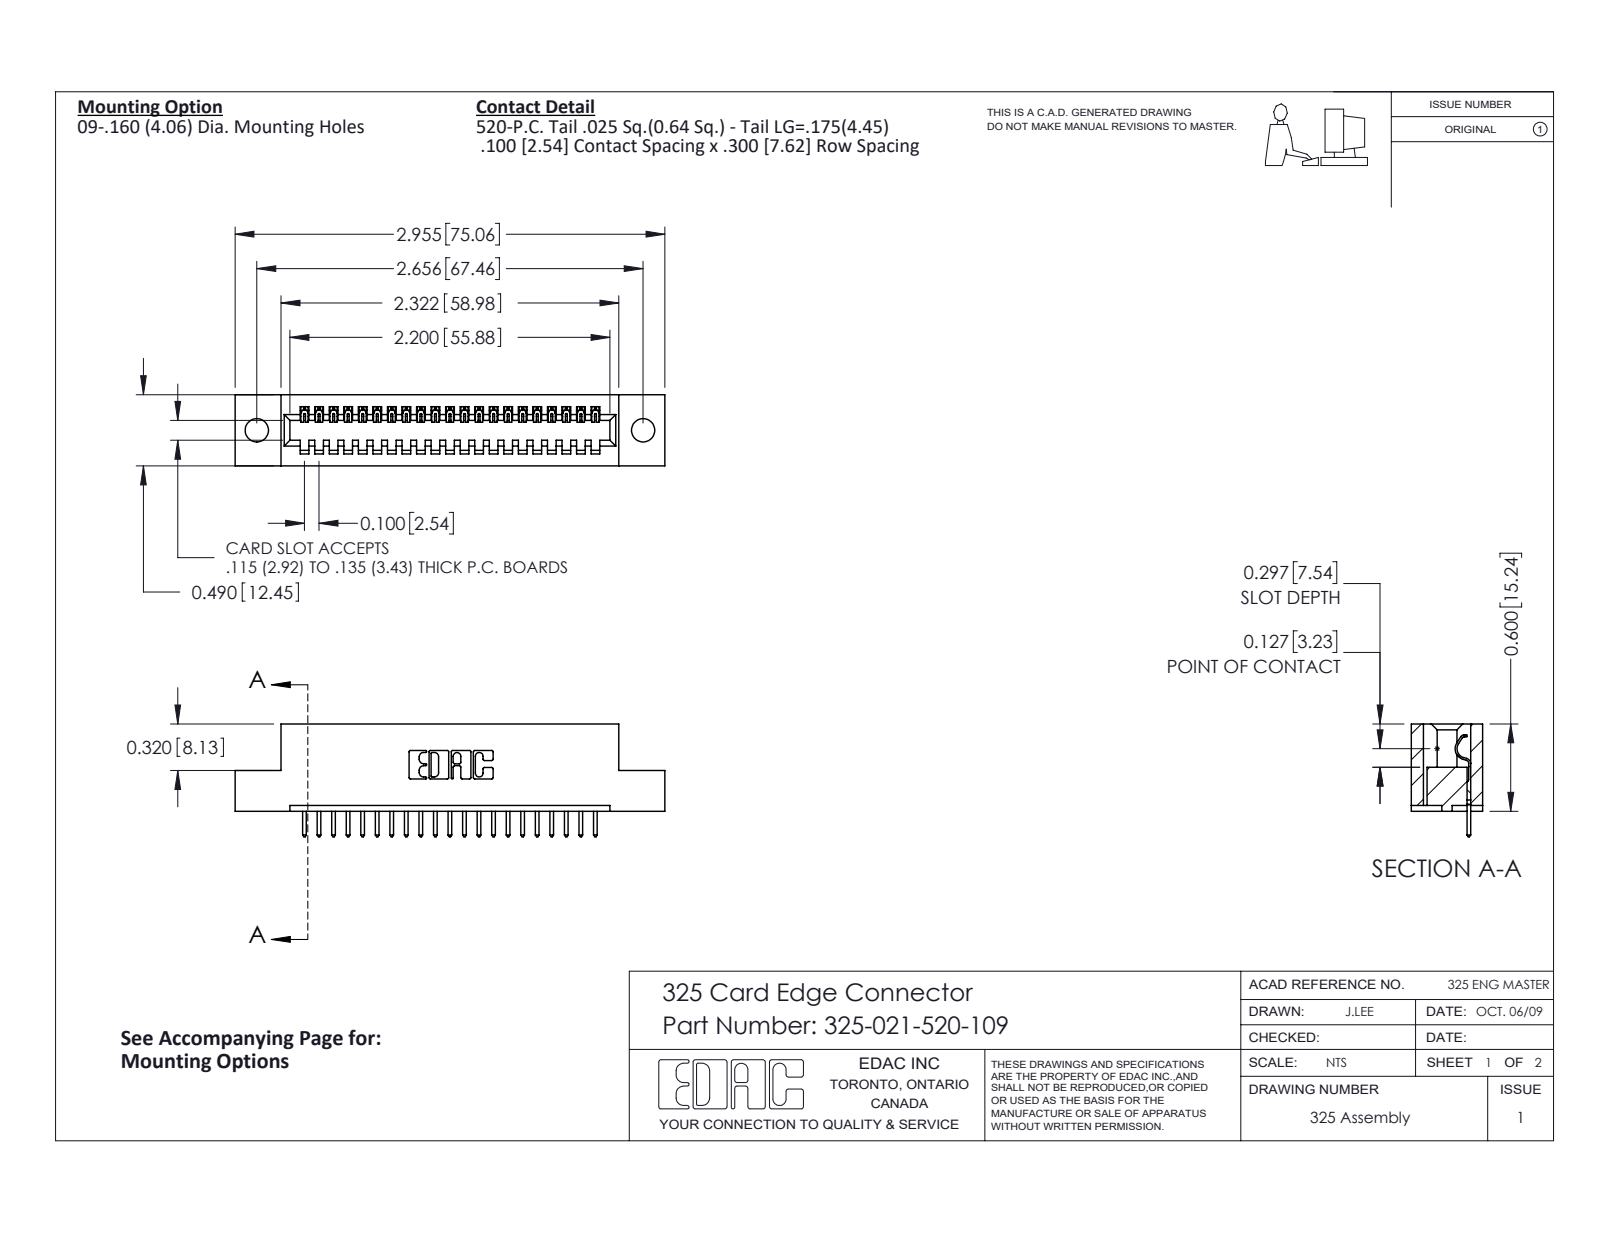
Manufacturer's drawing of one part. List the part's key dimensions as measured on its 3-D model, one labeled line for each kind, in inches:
Part name (STEP PRODUCT): 325-292-001_325-293-120; 325-021-520-109; 325 Part_.160 TH
STEP written by: SolidWorks 2016 (CONFIG_CONTROL_DESIGN)
Units: inches
Bodies: 22 solids, 1332 faces (952 planar, 380 cylindrical, 0 other)
Overall size (bounding box): 2.955 × 0.775 × 0.49
Volume: 0.554 in³ · Surface area: 14.32 in²
Round holes (diameter × count): ⌀0.16 ×2
Partial cylindrical surfaces — rounded edges, fillets, slot ends (radius × count): R0.006 ×42, R0.01 ×42, R0.01 ×22, R0.007 ×6, R0.031 ×6, R0.026 ×3, R0.014 ×1, R0.022 ×1
Main face-to-face distances: 0.083, 0.407, 0.49, 0.3, 0.107, 0.383, 0.025, 0.6, 0.04, 0.1
Hole centre spacings: 2.656
